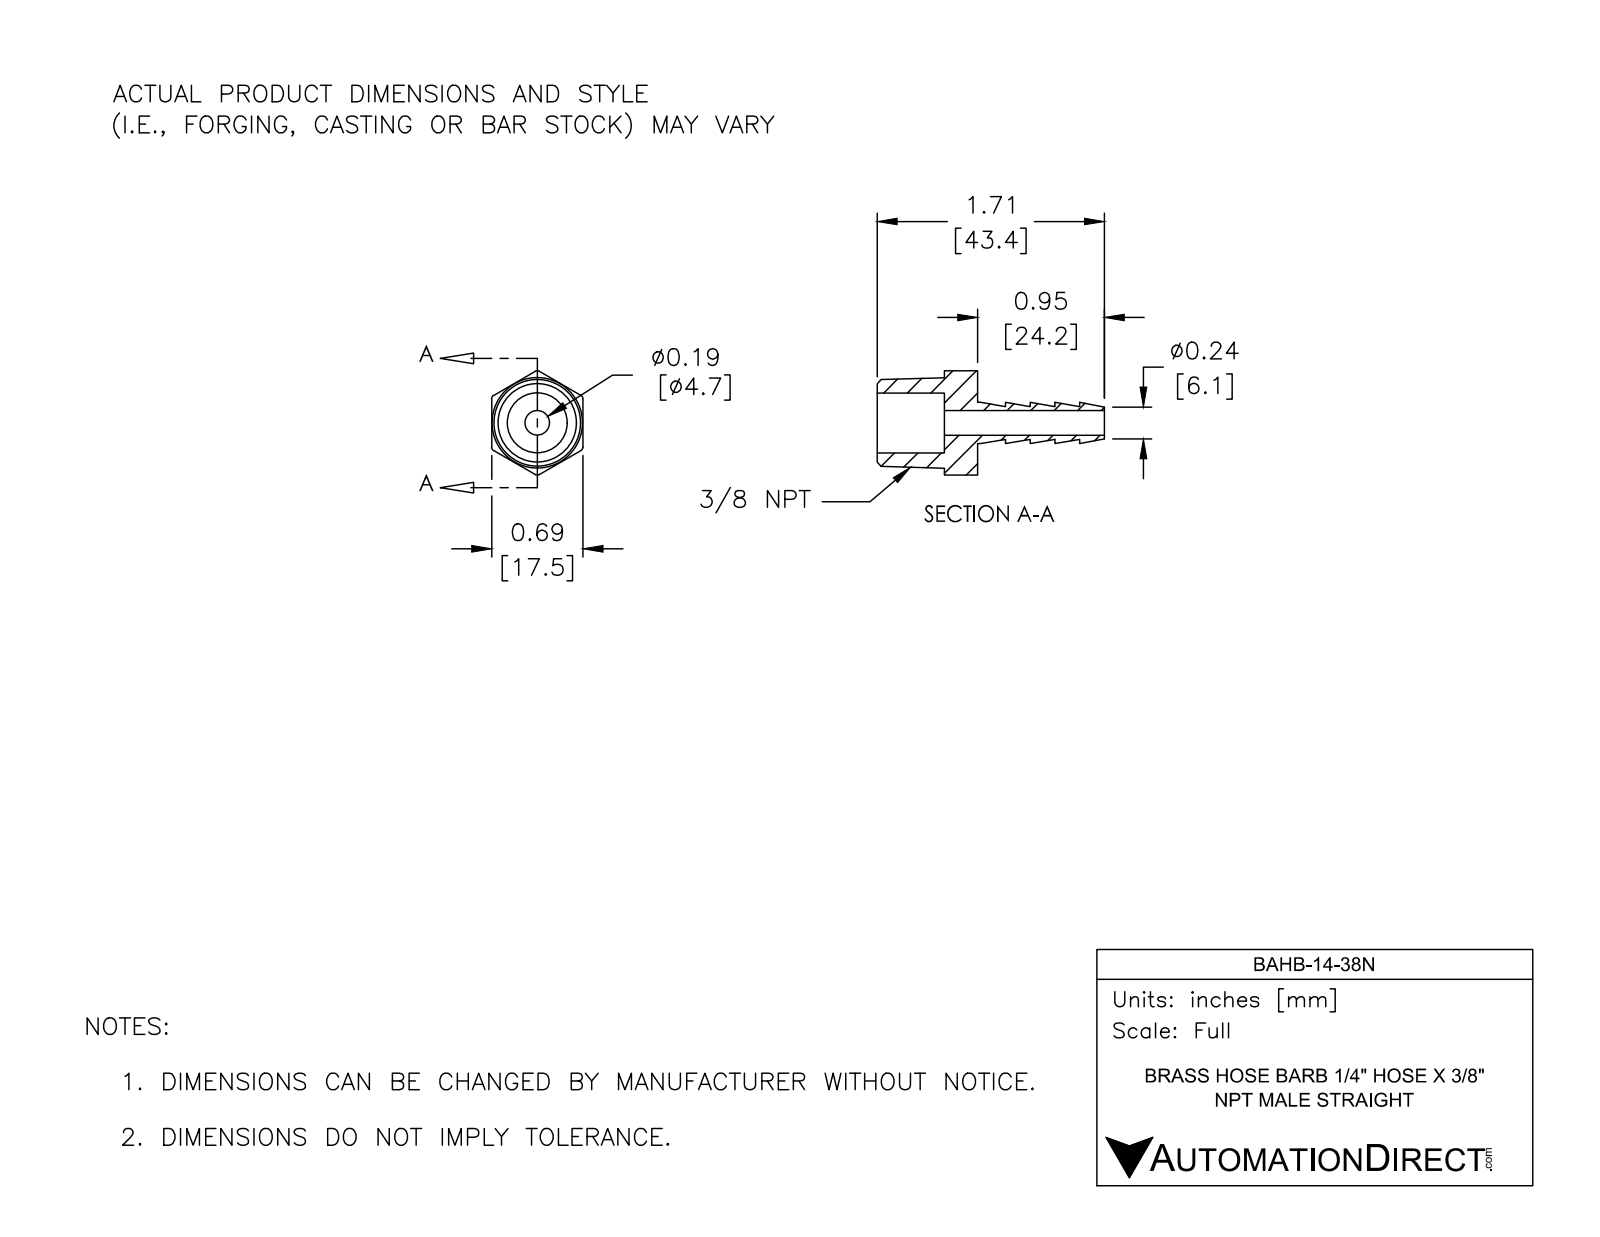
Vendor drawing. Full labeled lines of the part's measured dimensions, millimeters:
Part name (STEP PRODUCT): BAHB-14-38N
STEP written by: SolidWorks 2017 (AUTOMOTIVE_DESIGN)
Units: millimetres
Bodies: 1 solid, 41 faces (15 planar, 12 cylindrical, 14 other)
Overall size (bounding box): 43.4 × 19.9 × 17.4
Volume: 3 650 mm³ · Surface area: 3 030 mm²
Round holes (diameter × count): ⌀4.7 ×1, ⌀11.5 ×1
Round bosses / shafts (diameter × count): ⌀7.9 ×1
Partial cylindrical surfaces — rounded edges, fillets, slot ends (radius × count): R0.8 ×6
Main face-to-face distances: 17.4, 6.4, 19.2, 12.9, 9.4, 4.7, 4.7, 14.2, 19.5, 25.9
